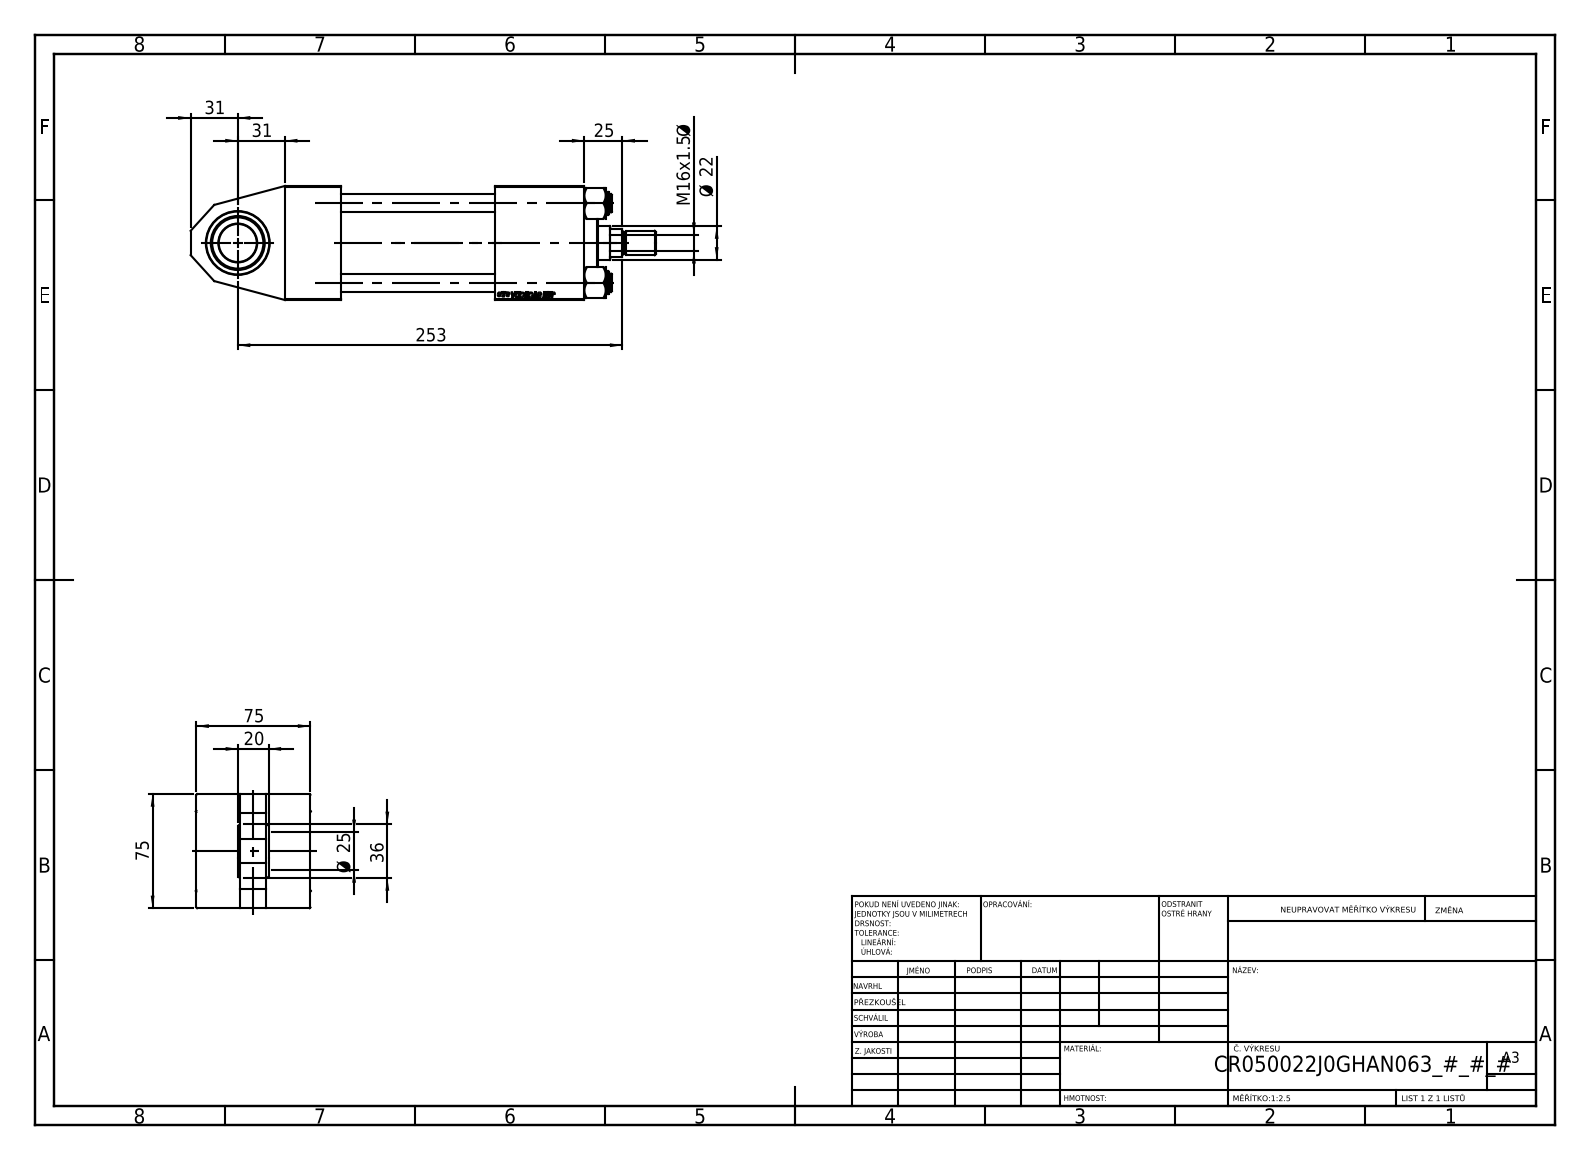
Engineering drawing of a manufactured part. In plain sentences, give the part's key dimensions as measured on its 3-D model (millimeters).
The part is named "V215CR_VCP_J; V215CR_J_Body; NUT_M5_J; V215CR_J_VNITRNI_KROUZEK (+3 more)". Its 3-D file was written by "SolidWorks 2019 (CONFIG_CONTROL_DESIGN)". It is 13 solids with 1159 faces: 520 planar, 93 cylindrical and 546 other. Overall it measures 306 by 75.54 by 75 millimeters. Its volume is 778 136 cubic millimeters and its surface area 188 867 square millimeters. Round holes: 4 of diameter 12, 2 of diameter 2.5, 2 of diameter 7, 2 of diameter 20.96, 2 of diameter 25, 2 of diameter 30, 1 of diameter 10.5, 1 of diameter 22, 1 of diameter 41, 1 of diameter 42, 1 of diameter 50, 1 of diameter 53. Round bosses or shafts: 4 of diameter 15, 1 of diameter 56, 1 of diameter 34, 1 of diameter 16, 1 of diameter 14. Partial cylindrical surfaces (rounded edges, fillets, slot ends): 1 of radius 10.5. The main face-to-face distances are 75, 29, 46, 160, 37, 197, 138, 101, 59, 17. The hole center spacings are 26.19, 36.98, 52.3, 57.22, 24.75, 49.5, 73.96, 136.5.
